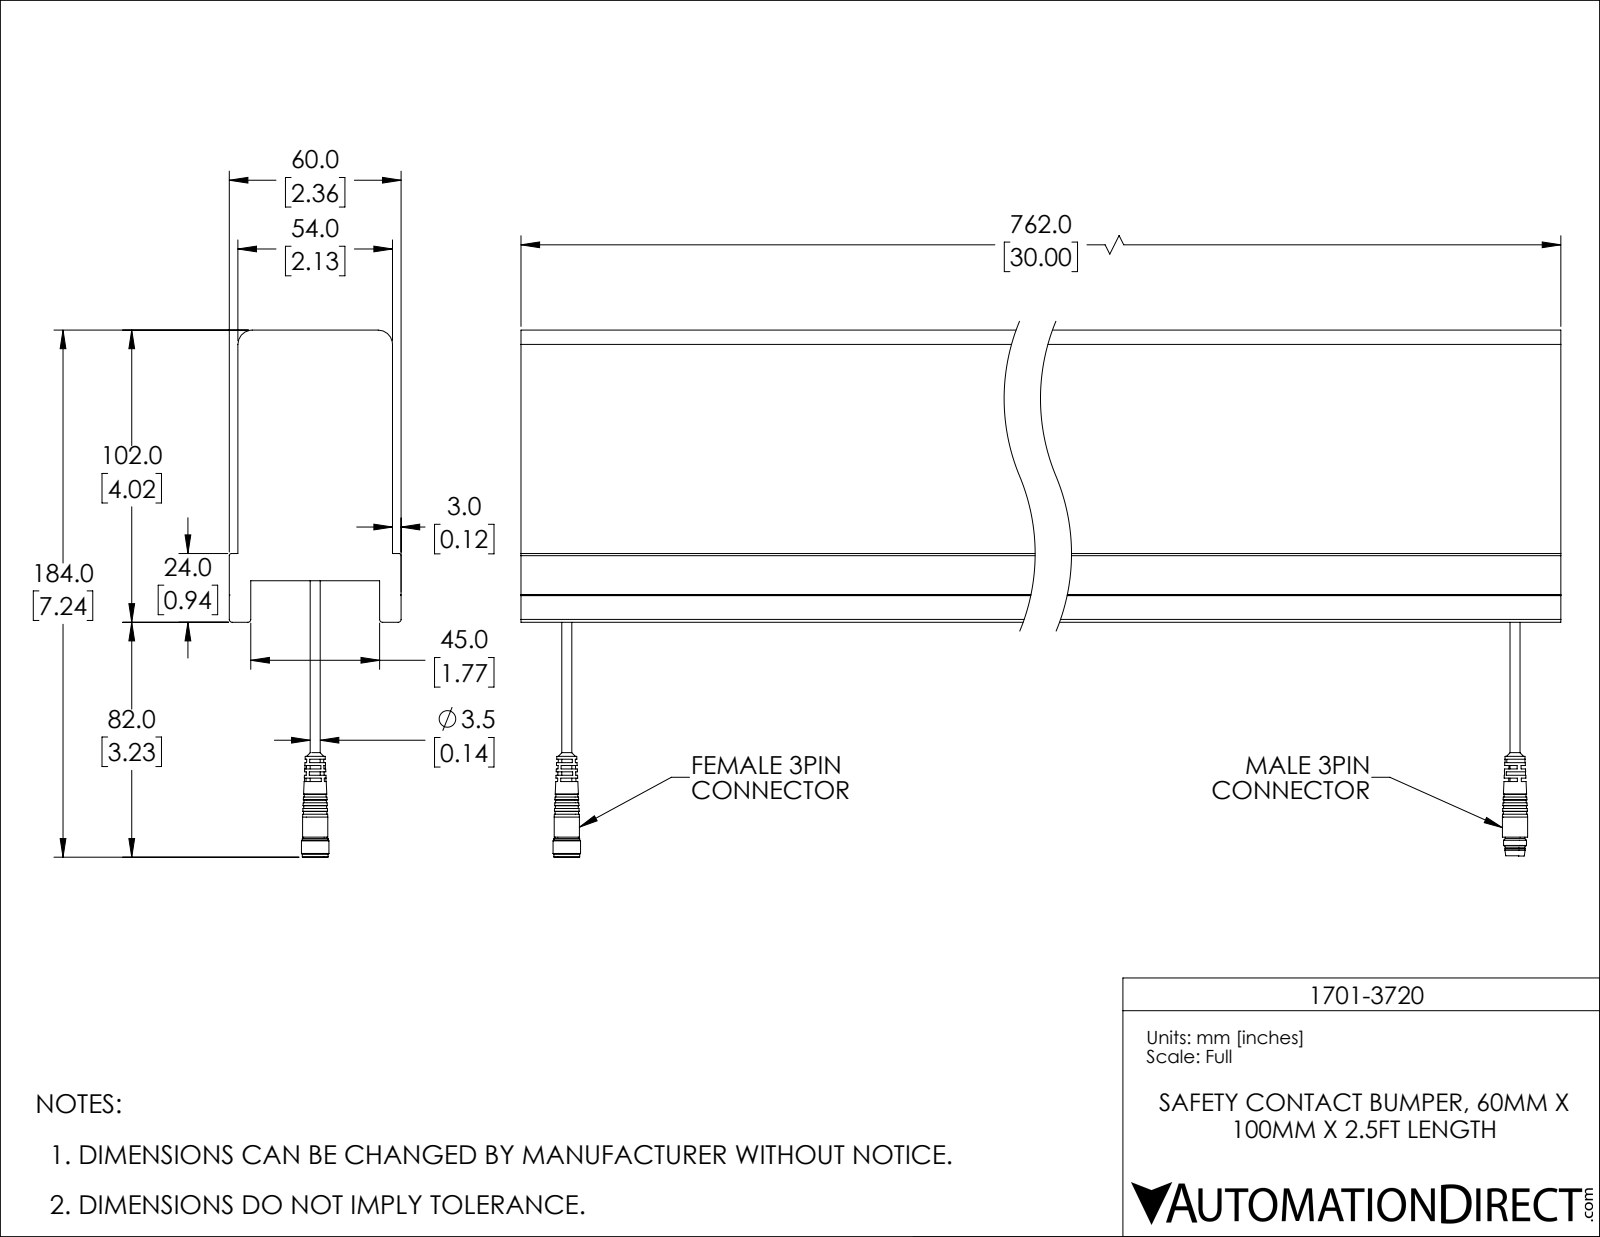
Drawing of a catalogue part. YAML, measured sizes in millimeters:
part_name: "1701-3720"
step_written_by: "SolidWorks 2018 (AUTOMOTIVE_DESIGN)"
units: millimeters
bodies: {solids: 20, faces: 294, planar: 138, cylindrical: 59, other: 97}
overall_size: [762, 184, 60]
volume: 3805000
surface_area: 279600
round_holes:
  - {diameter: 1.6, count: 3}
  - {diameter: 3.4, count: 2}
  - {diameter: 5.8, count: 1}
  - {diameter: 5.9, count: 1}
  - {diameter: 6.9, count: 1}
  - {diameter: 7.2, count: 1}
round_bosses_or_shafts:
  - {diameter: 1.2, count: 16}
  - {diameter: 0.8, count: 4}
  - {diameter: 1, count: 3}
  - {diameter: 8.8, count: 2}
  - {diameter: 3.5, count: 2}
  - {diameter: 9.6, count: 1}
  - {diameter: 9, count: 1}
  - {diameter: 8, count: 1}
face_to_face_distances: [54, 87.5, 3, 57, 7.5, 52.5, 4.5, 49.5, 60, 45]
hole_center_spacings: [1.8, 2.5, 731.2, 3.5, 728.8, 730]
